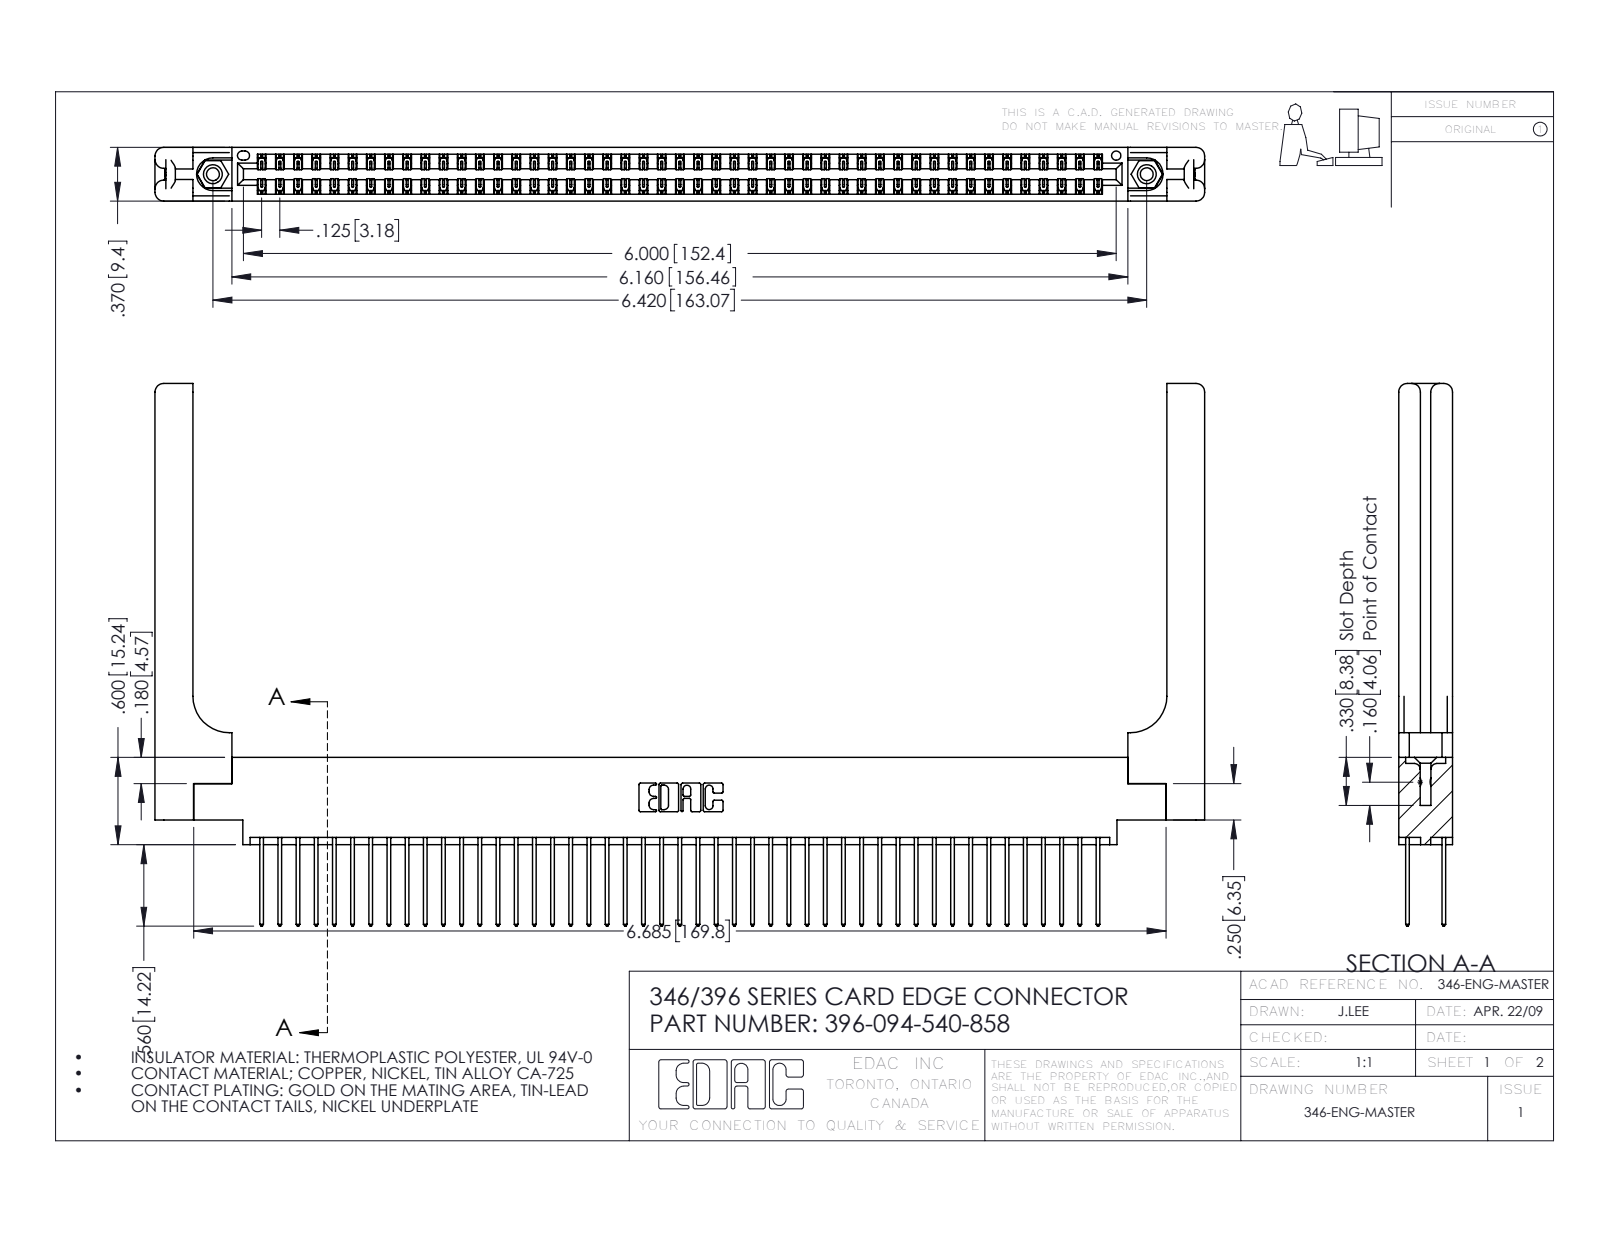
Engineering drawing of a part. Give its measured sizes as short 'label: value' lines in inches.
name: 396-094-540-858; 346-220-058_345-220-058; 345-292-001_345-293-140; 345-250-001_345-250-001-102 (+1 more)
written by: SolidWorks 2016 (CONFIG_CONTROL_DESIGN)
unit: in
bodies: 99 solids, 5270 faces (3518 planar, 1692 cylindrical, 60 other)
size: 7.216 × 3.73 × 0.37
volume: 1.563 in³; area: 49.31 in²
holes: 2× ⌀0.089, 2× ⌀0.125, 2× ⌀0.156, 1× ⌀0.064
bosses: 2× ⌀0.155
rounds: 141× R0.006, 94× R0.01, 22× R0.01, 16× R0.06, 6× R0.007, 6× R0.031, 3× R0.026, 2× R0.014
face distances: 0.048, 0.322, 0.37, 0.072, 0.25, 0.025, 0.298, 0.148, 0.15, 0.275
hole spacings: 0.246, 6.211, 6.42
